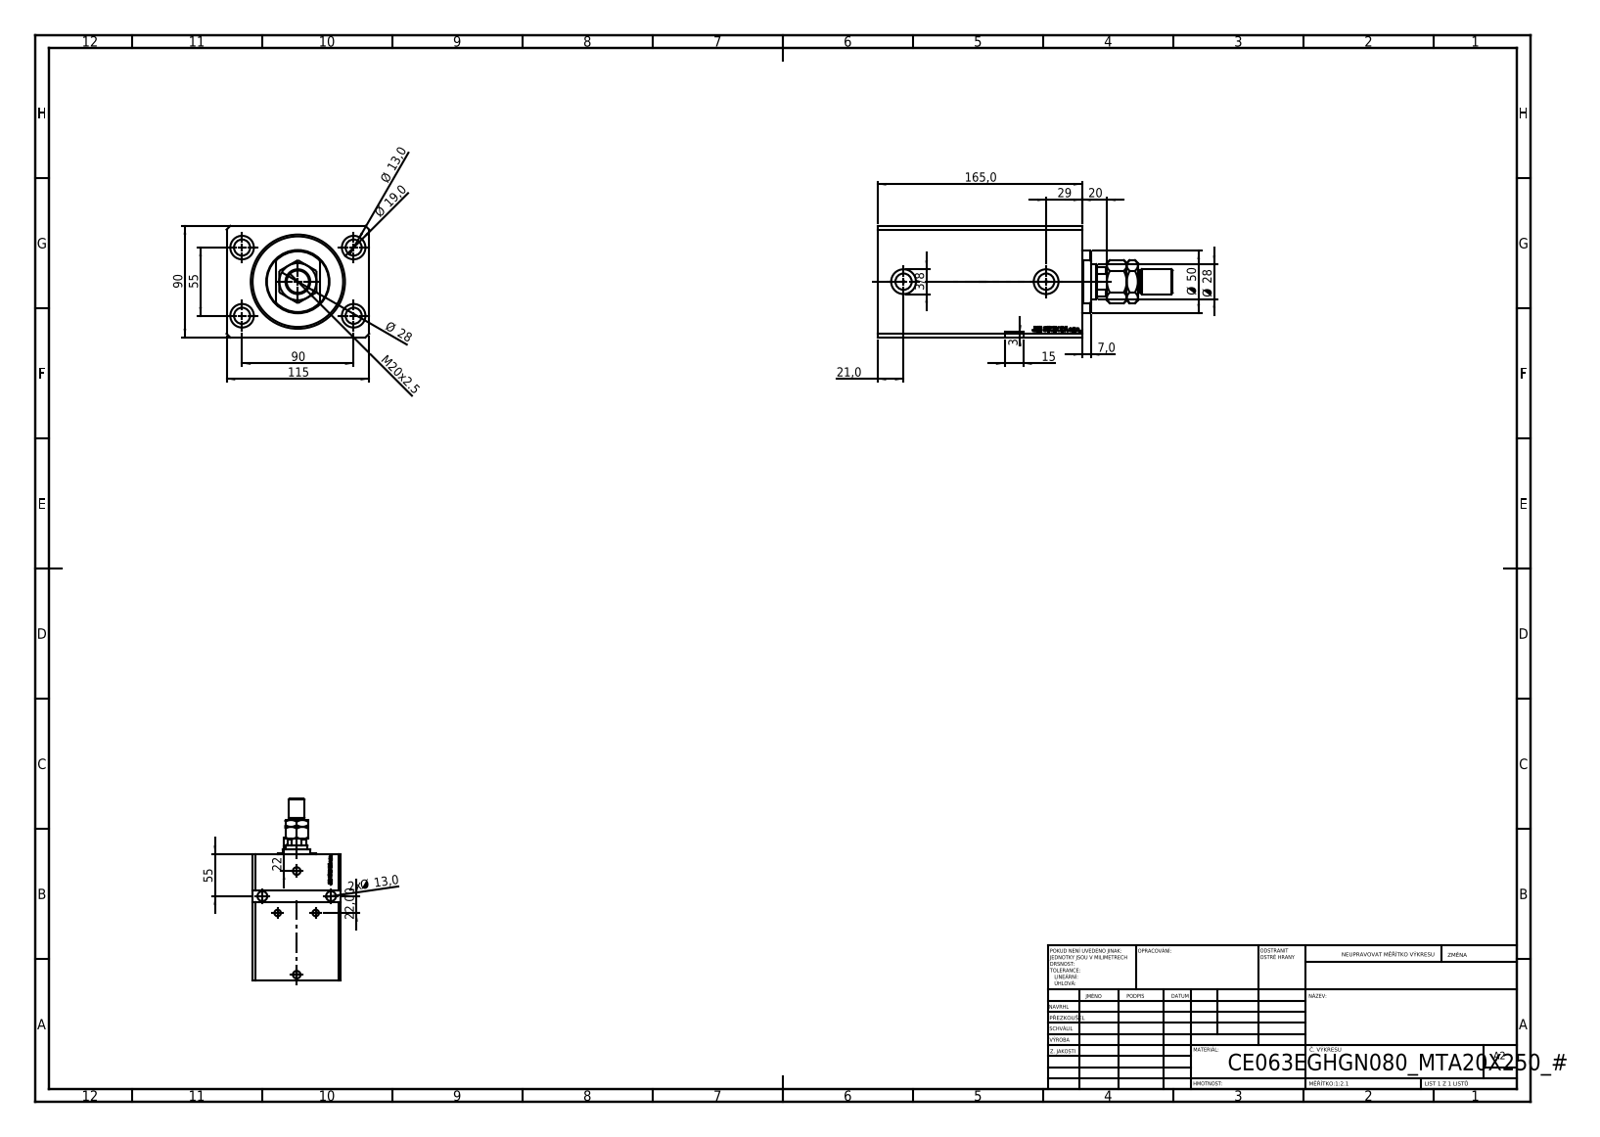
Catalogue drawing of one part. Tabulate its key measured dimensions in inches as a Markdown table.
| quantity | value |
| --- | --- |
| part name | V250CE_C_VCP; MTA; V250CE_E_Body; V250CE_VC_E |
| STEP written by | SolidWorks 2019 (CONFIG_CONTROL_DESIGN) |
| units | inches |
| bodies | 4 solids, 994 faces (482 planar, 96 cylindrical, 416 other) |
| overall size | 9.37 × 4.528 × 3.543 |
| volume | 85.62 in³ |
| surface area | 315.3 in² |
| round holes (diameter × count) | 0.512 × 6, 0.049 × 4, 0.748 × 4, 0.335 × 2, 0.394 × 2, 0.518 × 2, 0.787 × 2, 0.728 × 1, 1.102 × 1, 2.48 × 1, 2.992 × 1 |
| round bosses / shafts (diameter × count) | 1.969 × 1, 0.787 × 1, 0.709 × 1 |
| partial cylindrical surfaces (radius × count) | 0.531 × 1 |
| main face-to-face distances | 3.543, 4.528, 0.787, 6.496, 0.705, 5.791, 5.709, 5.004, 2.559, 3.15 |
| hole center spacings | 2.076, 3.543, 1.17, 2.165, 2.197, 2.379, 2.889, 3.317 |
